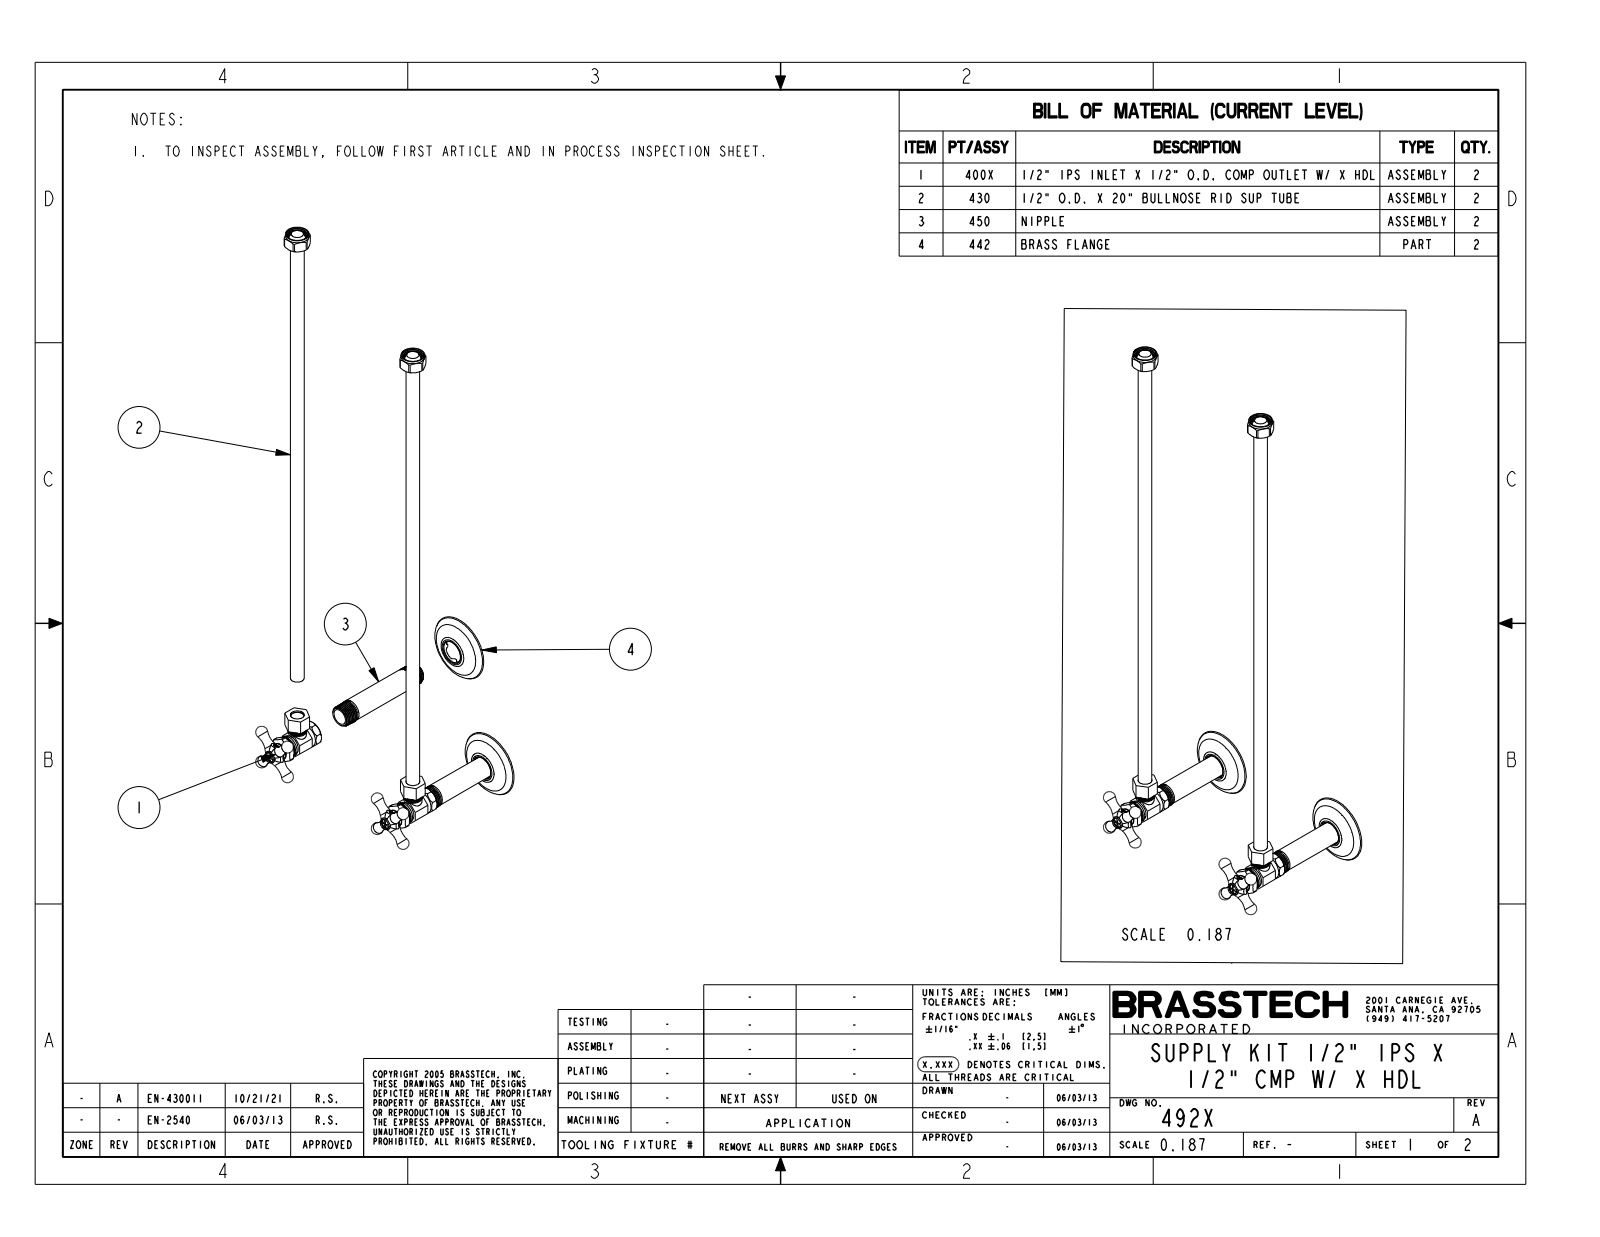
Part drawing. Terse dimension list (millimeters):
name: 492X
written by: CREO PARAMETRIC BY PTC INC, 2018500 (CONFIG_CONTROL_DESIGN)
unit: mm
bodies: 10 solids, 1564 faces (392 planar, 546 cylindrical, 626 other)
size: 549.9 × 215.9 × 151.7
volume: 86 280 mm³; area: 221 300 mm²
holes: 2× ⌀3.3, 2× ⌀9.5, 2× ⌀10, 2× ⌀10.2, 2× ⌀11.4, 2× ⌀11.8, 2× ⌀12.2, 2× ⌀13.1, 2× ⌀13.2, 2× ⌀15.1, 2× ⌀16.3, 2× ⌀17.4
bosses: 2× ⌀22, 2× ⌀21.8, 2× ⌀20.6, 2× ⌀19.1, 2× ⌀17.3, 2× ⌀17.2, 2× ⌀16.6, 2× ⌀16
rounds: 36× R0.3, 12× R1.3, 6× R3.8, 2× R4.3, 2× R8.6, 2× R9.6, 2× R12.4, 1× R4.8
face distances: 20.6, 22.2, 76.2, 152.4, 22.9, 132, 1.1, 21.7, 475.2, 13.5
hole spacings: 152.4, 28.3, 155
